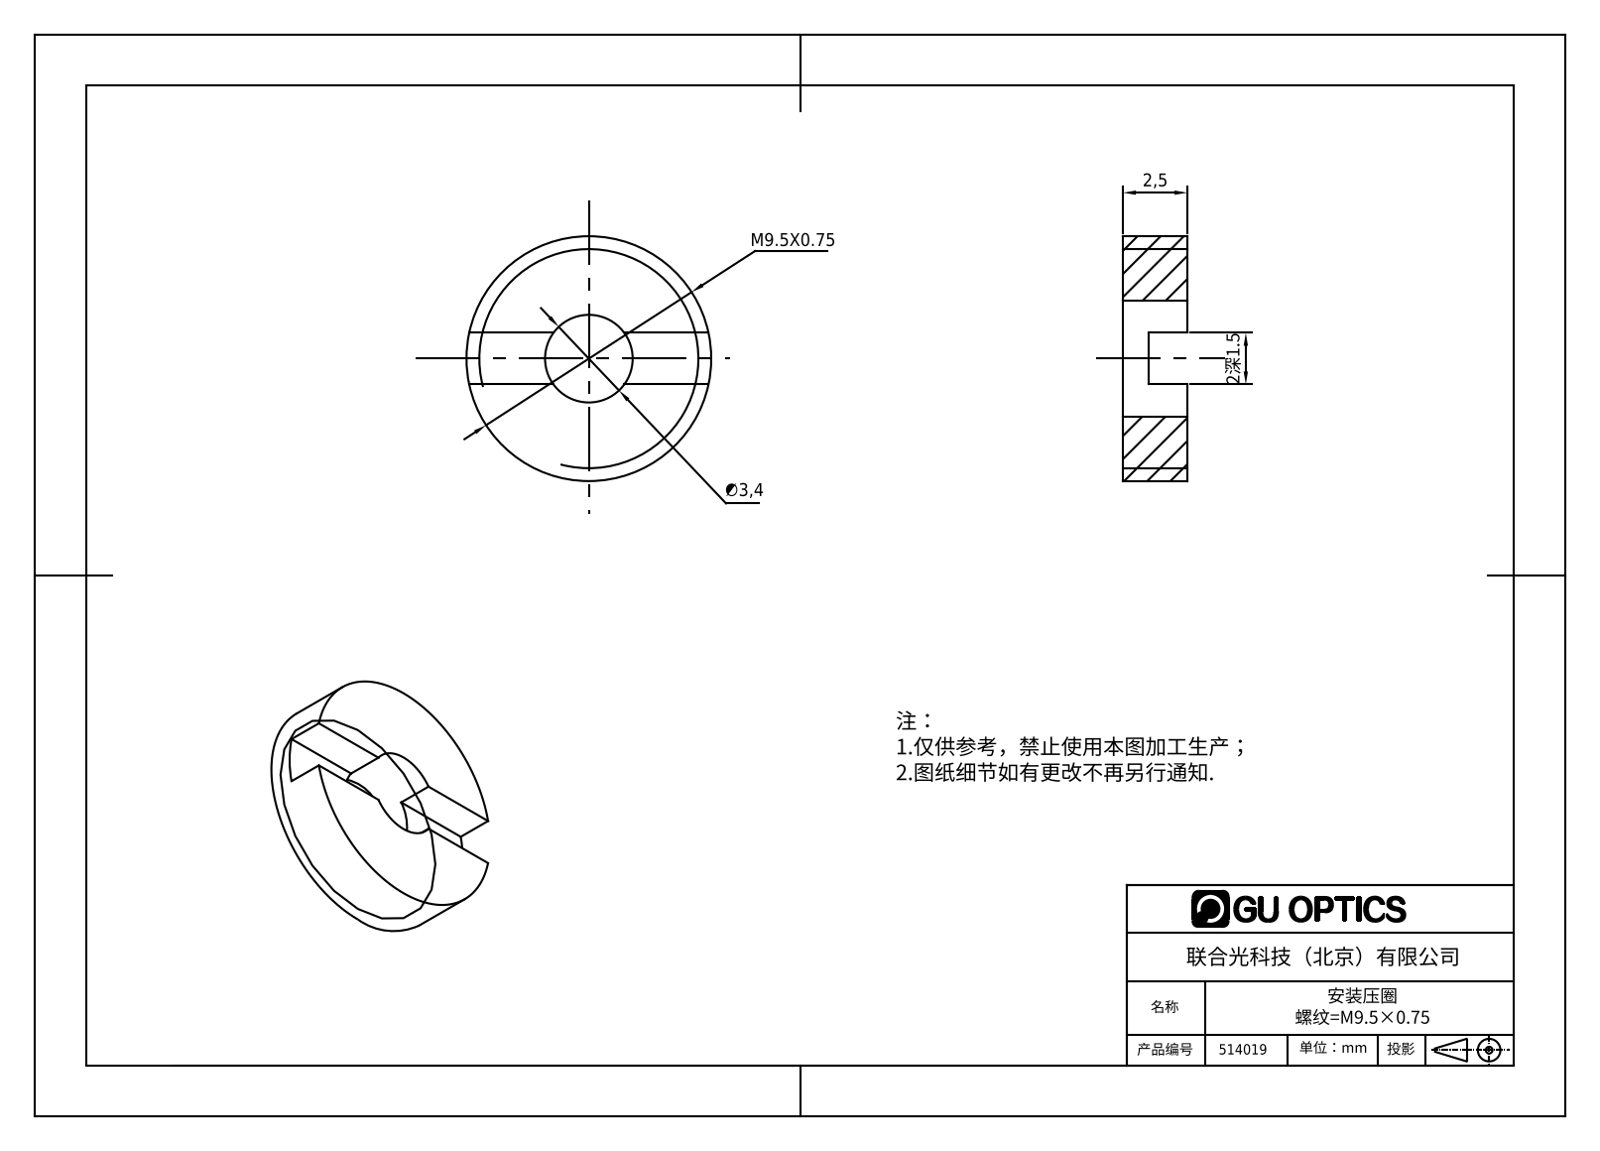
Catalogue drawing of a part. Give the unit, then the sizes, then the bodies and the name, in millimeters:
Units: millimetres
Overall size (bounding box): 9.5 × 9.5 × 2.5
Round holes (diameter × count): ⌀3.4 ×1
Round bosses / shafts (diameter × count): ⌀9.5 ×1
Main face-to-face distances: 2.5, 1, 1.5, 2
Volume: 136 mm³ · Surface area: 232 mm²
Bodies: 1 solid, 13 faces (9 planar, 4 cylindrical, 0 other)
Part name (STEP PRODUCT): 514019
STEP written by: SolidWorks 2016 (CONFIG_CONTROL_DESIGN)
